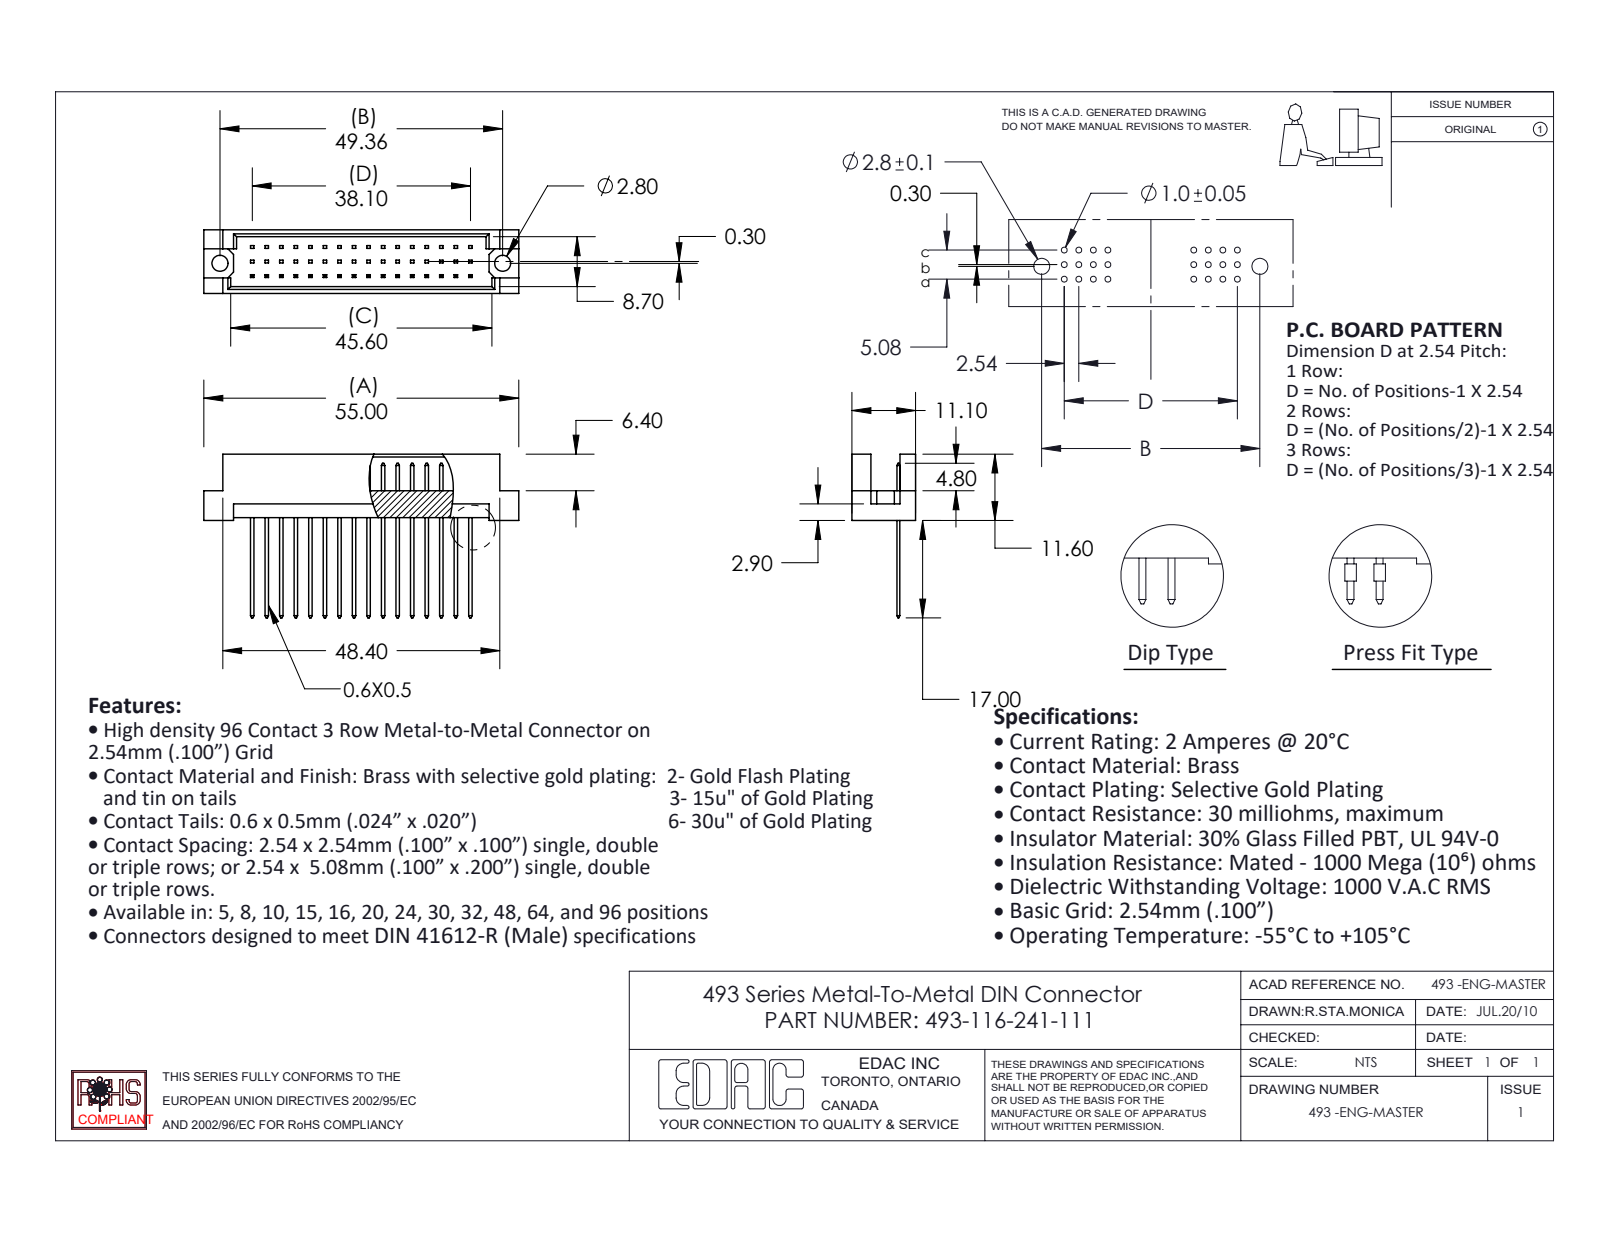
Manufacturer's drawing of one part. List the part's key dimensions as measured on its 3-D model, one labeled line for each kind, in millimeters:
Part name (STEP PRODUCT): 493-290_41; 493 Part_48; 493-116-241-112
STEP written by: SolidWorks 2020 (CONFIG_CONTROL_DESIGN)
Units: millimetres
Bodies: 17 solids, 468 faces (464 planar, 4 cylindrical, 0 other)
Overall size (bounding box): 55 × 28.6 × 11.1
Volume: 3 400 mm³ · Surface area: 4 701 mm²
Round holes (diameter × count): ⌀2.8 ×2
Main face-to-face distances: 1.2, 9.9, 11.1, 0.5, 2.54, 8.7, 5.08, 4.7, 2.76, 8.34
Hole centre spacings: 49.36
